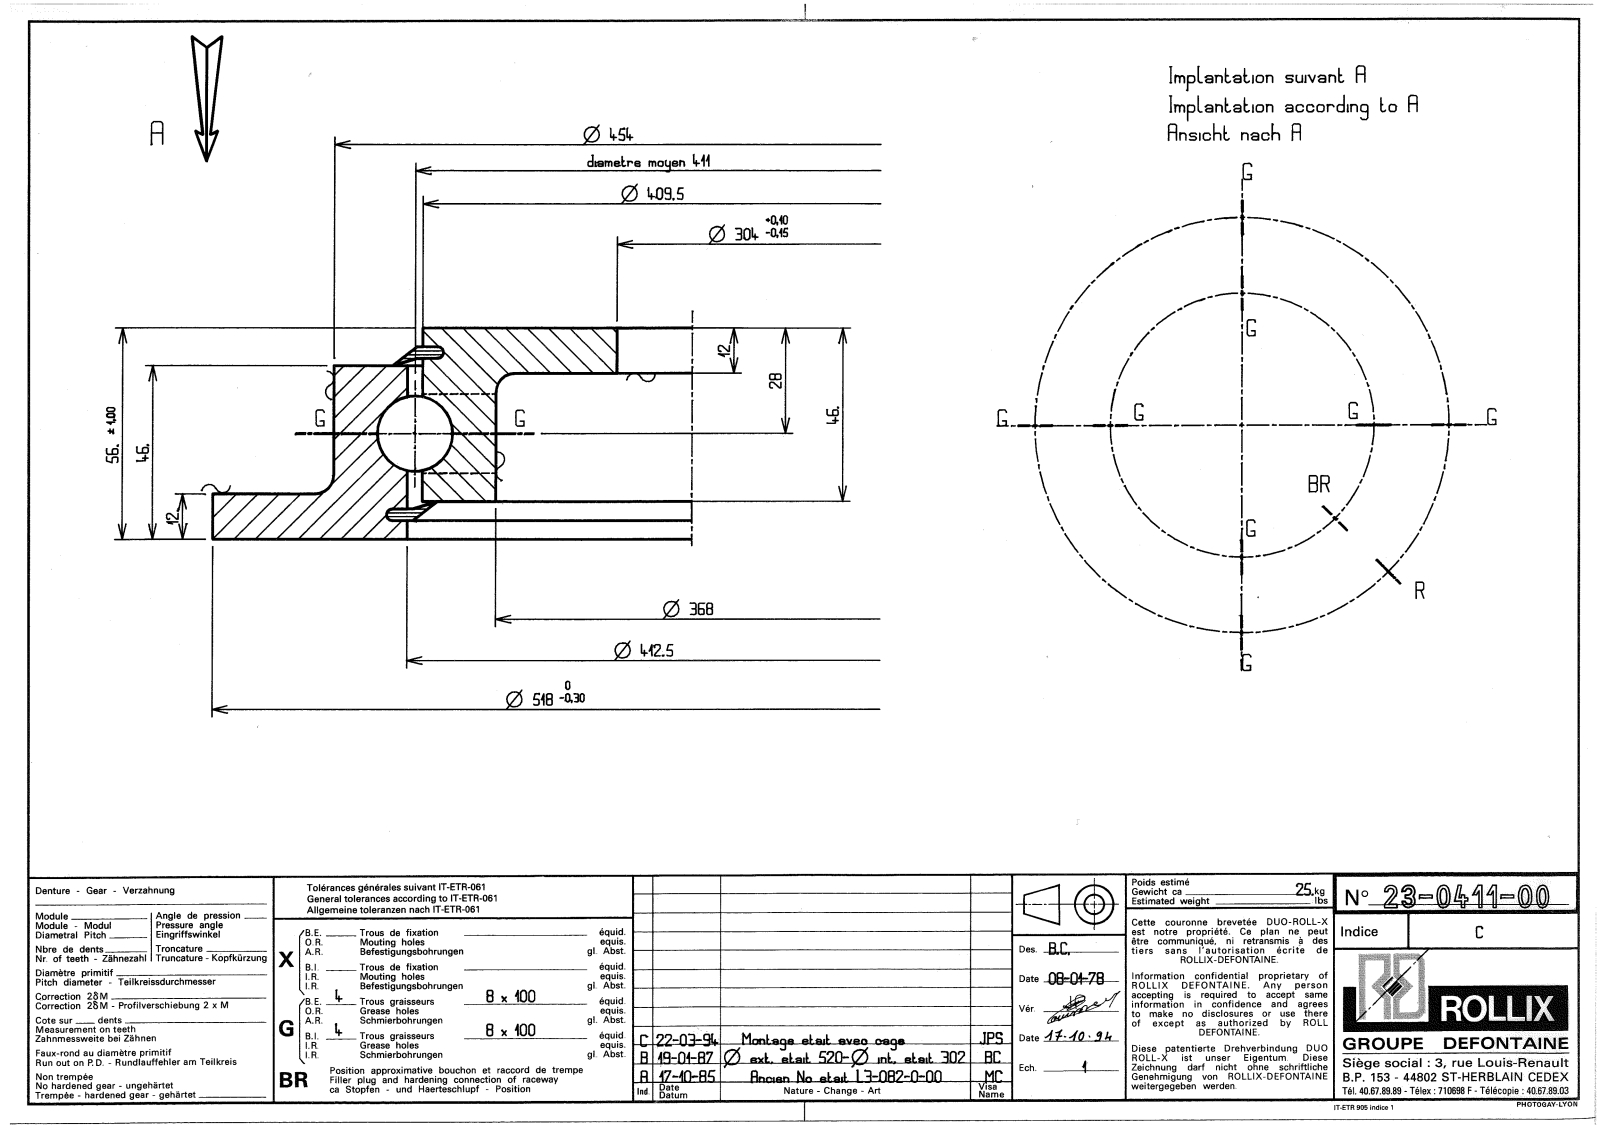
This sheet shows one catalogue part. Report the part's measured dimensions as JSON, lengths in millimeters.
{"part_name": "23-0411-00", "step_written_by": "SolidWorks 2016 (CONFIG_CONTROL_DESIGN)", "units": "millimeters", "bodies": {"solids": 13, "faces": 258, "planar": 94, "cylindrical": 52, "other": 112}, "overall_size": [518, 518, 56], "volume_mm3": 3064000, "surface_area_mm2": 621179, "round_holes": [[7, 8], [304, 1], [368, 1], [415.5, 1]], "round_bosses_or_shafts": [[8, 8], [518, 1], [454, 1], [406.5, 1]], "face_to_face_distances": [12, 44, 56, 10, 46, 2, 34, 32, 36, 4.95]}
